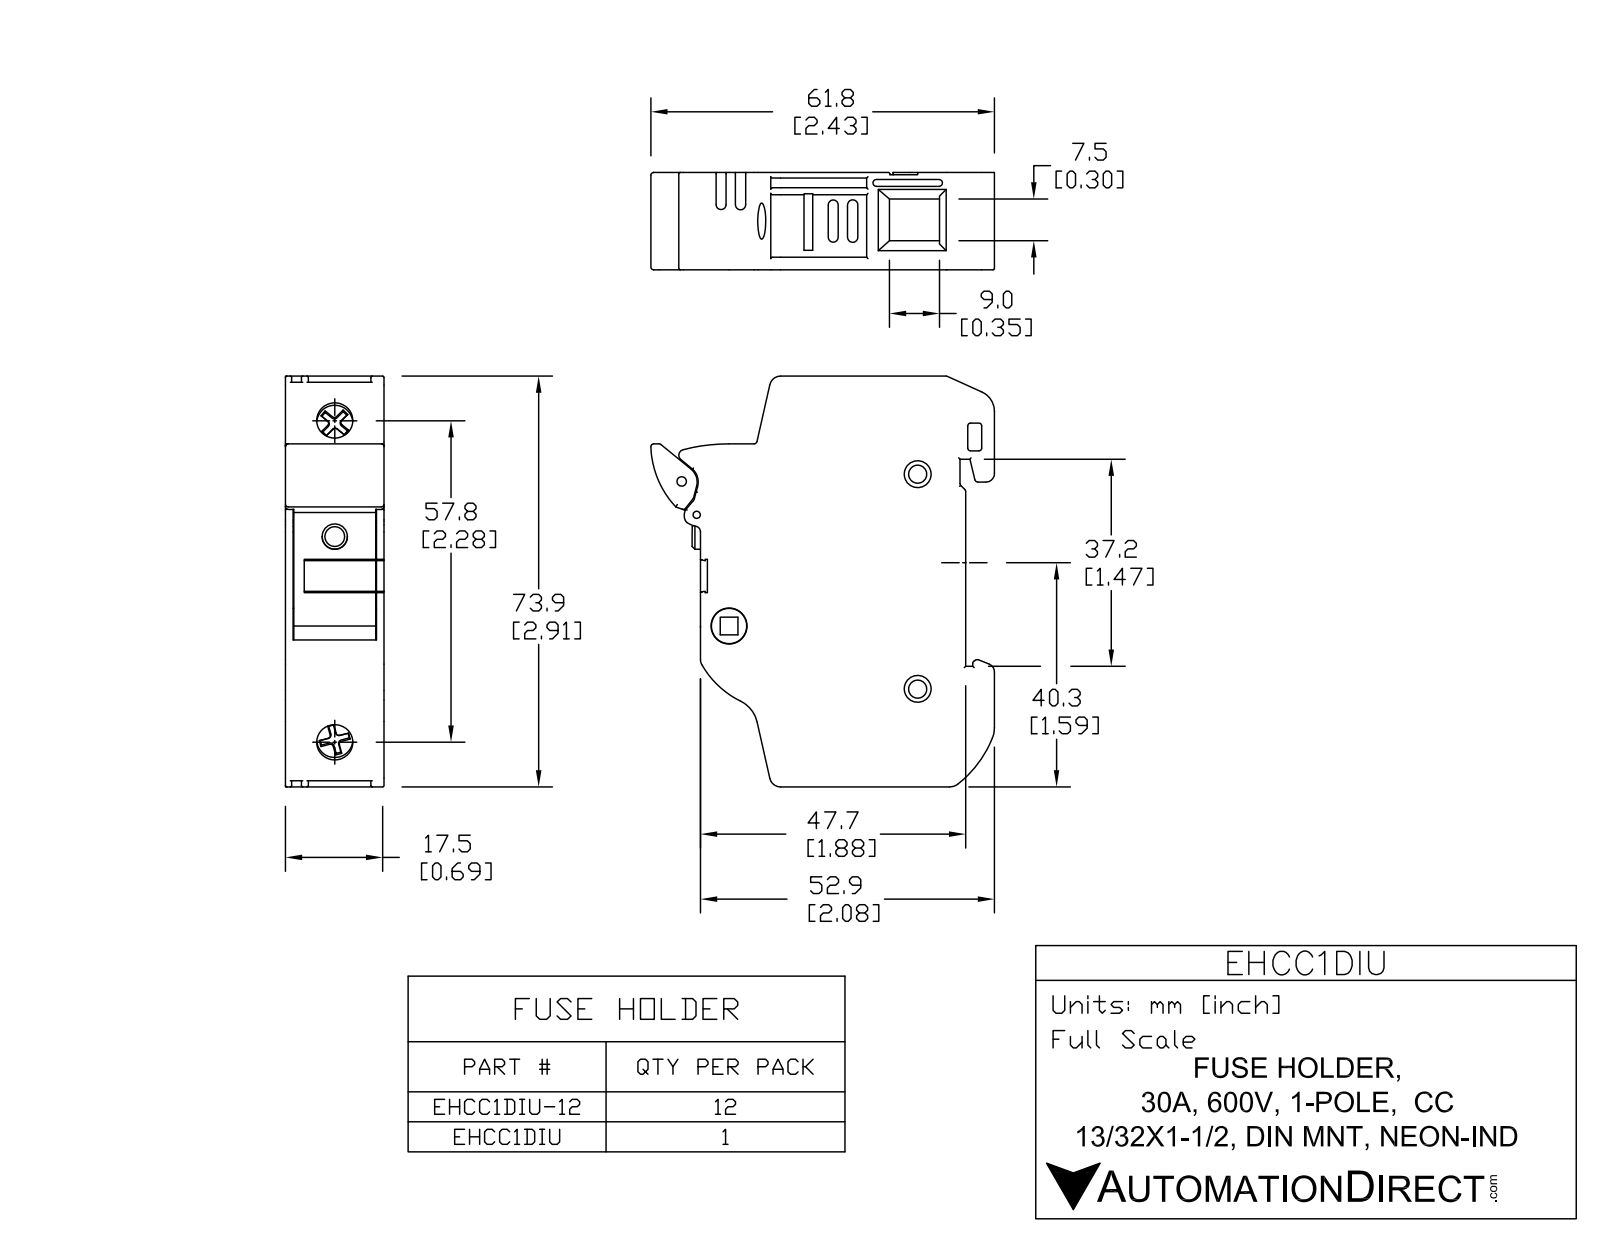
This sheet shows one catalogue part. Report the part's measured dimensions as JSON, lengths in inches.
{"part_name": "EHCC1DIU", "step_written_by": "SolidWorks 2011 (AUTOMOTIVE_DESIGN)", "units": "inches", "bodies": {"solids": 2, "faces": 595, "planar": 247, "cylindrical": 198, "other": 150}, "overall_size": [2.909, 2.434, 0.689], "volume_in3": 3.219, "surface_area_in2": 30.36, "round_holes": [[0.128, 2], [0.19, 2], [0.256, 2], [0.051, 1], [0.067, 1], [0.255, 1]], "round_bosses_or_shafts": [[0.25, 1], [0.179, 1]], "partial_cylinders_radius": [[0.01, 60], [0.02, 21], [0.079, 10], [0.02, 9], [0.039, 7], [0.024, 4], [0.035, 3], [0.036, 3]], "face_to_face_distances": [0.689, 0.049, 0.062, 0.64, 0.054, 0.635, 0.586, 1.083, 1.145, 0.903], "hole_center_spacings": [0.259, 0.82, 1.077, 1.408, 1.409, 1.52, 1.522, 1.592]}
